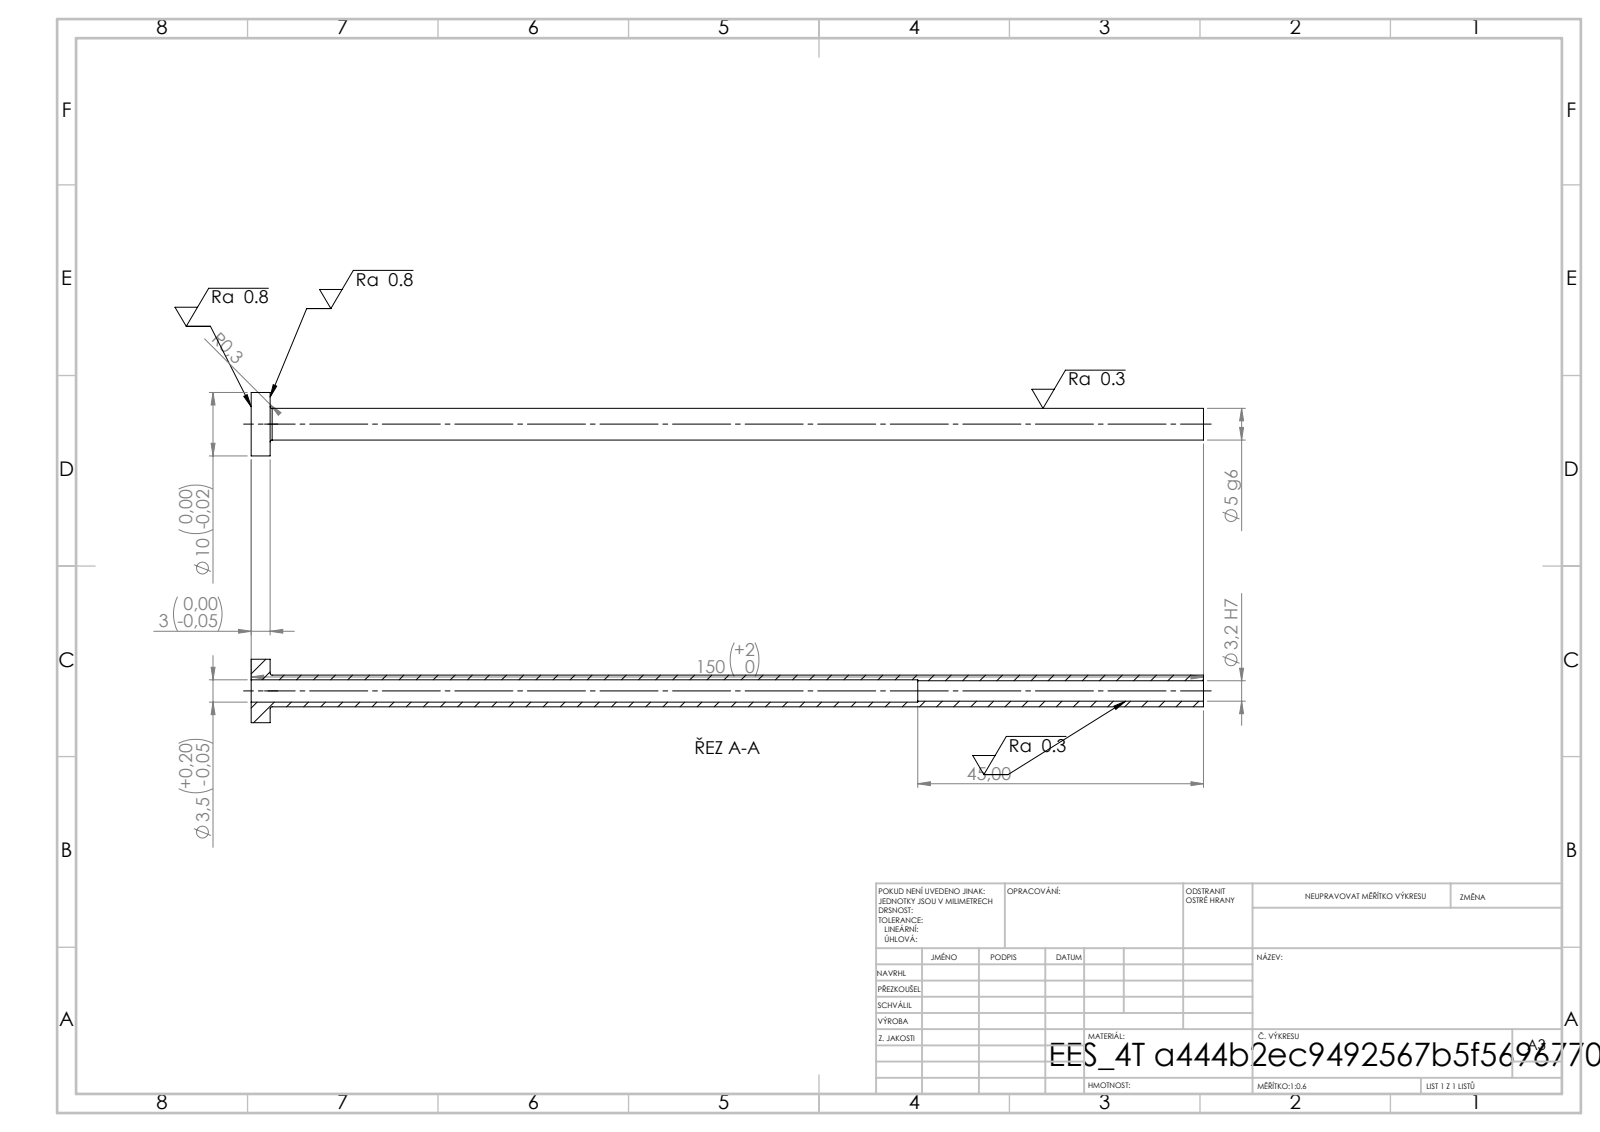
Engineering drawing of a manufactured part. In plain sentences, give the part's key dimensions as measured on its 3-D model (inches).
Its 3-D file was written by "SolidWorks 2019 (CONFIG_CONTROL_DESIGN)". It is 1 solid with 14 faces: 4 planar, 8 cylindrical and 2 other. Overall it measures 5.906 by 0.394 by 0.394 inches. Its volume is 0.107 cubic inches and its surface area 6.431 square inches. Round holes: 1 of diameter 0.126, 1 of diameter 0.138. Round bosses or shafts: 1 of diameter 0.394, 1 of diameter 0.197. The main face-to-face distances are 0.118, 5.906, 5.787, 4.134, 4.016, 1.772.
